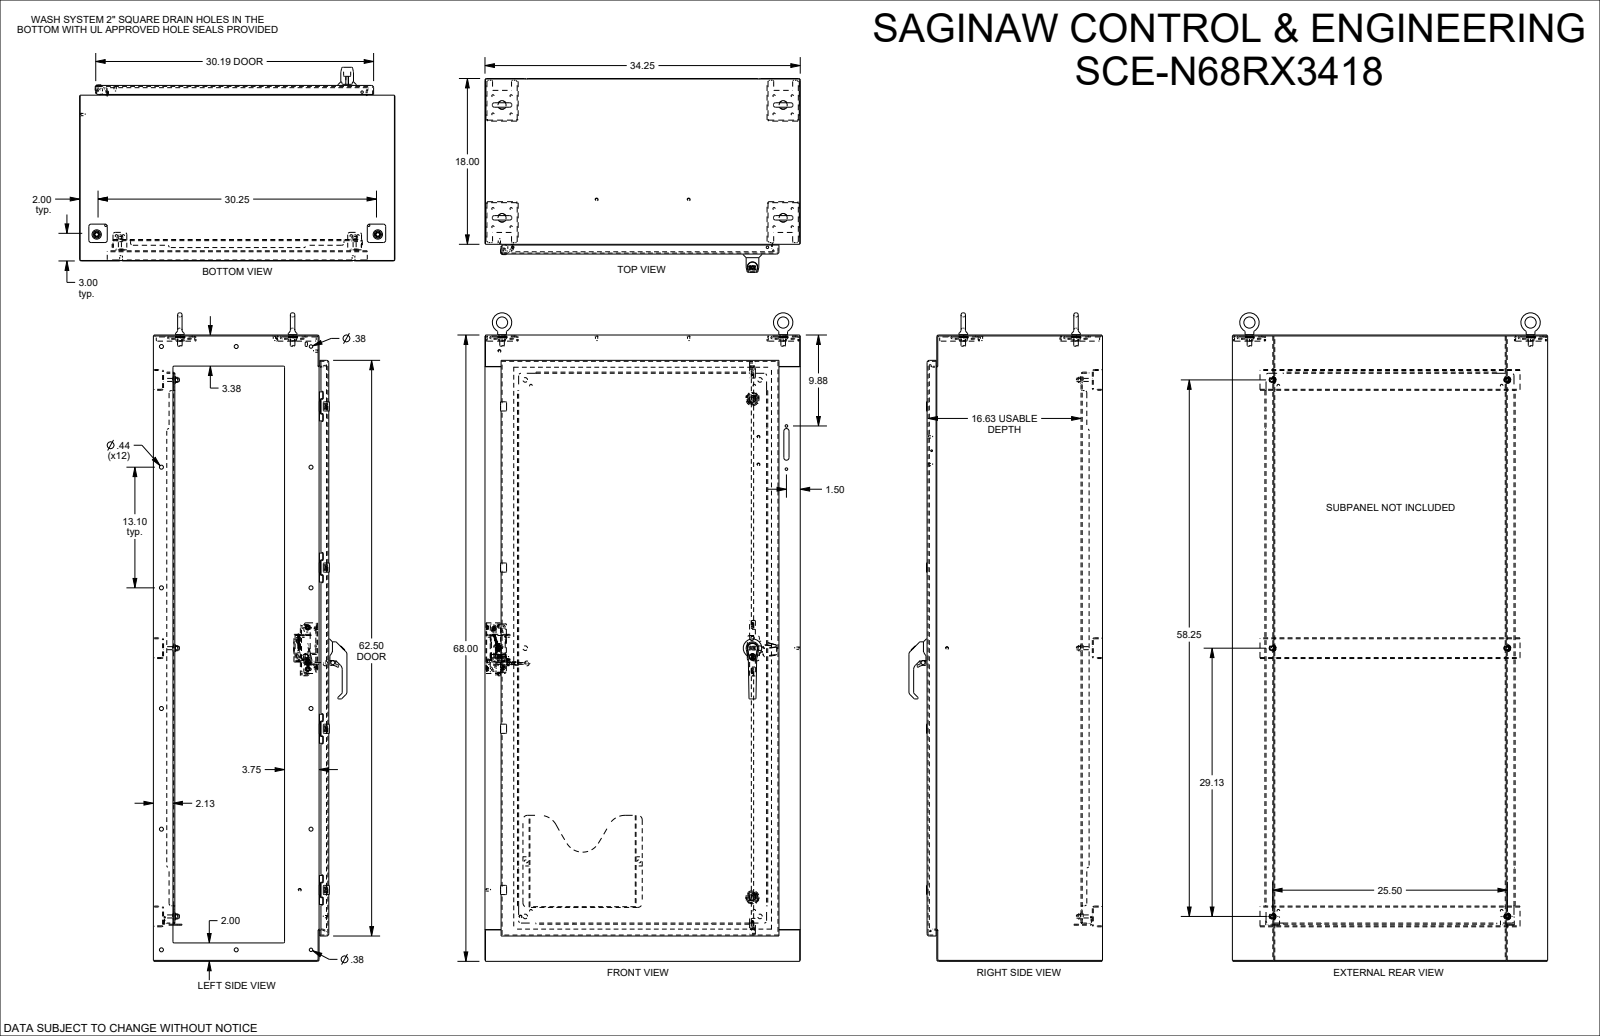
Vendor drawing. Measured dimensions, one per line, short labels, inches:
name: SCE-N68RX3418
written by: SolidWorks 2023 (AUTOMOTIVE_DESIGN)
unit: in
bodies: 31 solids, 4336 faces (1676 planar, 1540 cylindrical, 1120 other)
size: 70.945 × 34.25 × 21.046
volume: 942 in³; area: 17 745 in²
holes: 18× ⌀0.25, 12× ⌀0.437, 10× ⌀0.375, 8× ⌀0.205, 8× ⌀0.244, 4× ⌀0.04, 4× ⌀0.17, 4× ⌀0.218, 4× ⌀0.256, 4× ⌀0.875, 3× ⌀0.115, 3× ⌀0.2
bosses: 12× ⌀0.17, 10× ⌀0.25, 8× ⌀0.24, 5× ⌀0.196, 4× ⌀1.173, 4× ⌀0.6, 2× ⌀1.4, 2× ⌀0.48
rounds: 145× R0.03, 108× R0.015, 83× R0.125, 52× R0.062, 39× R0.04, 38× R0.167, 32× R0.229, 26× R0.25
face distances: 0.104, 18.954, 18.85, 19.058, 0.104, 17.896, 1.058, 67.896, 34.146, 67.792
hole spacings: 1.979, 1.4, 17.5, 13.1, 20.873, 2.799, 11.304, 12.25
